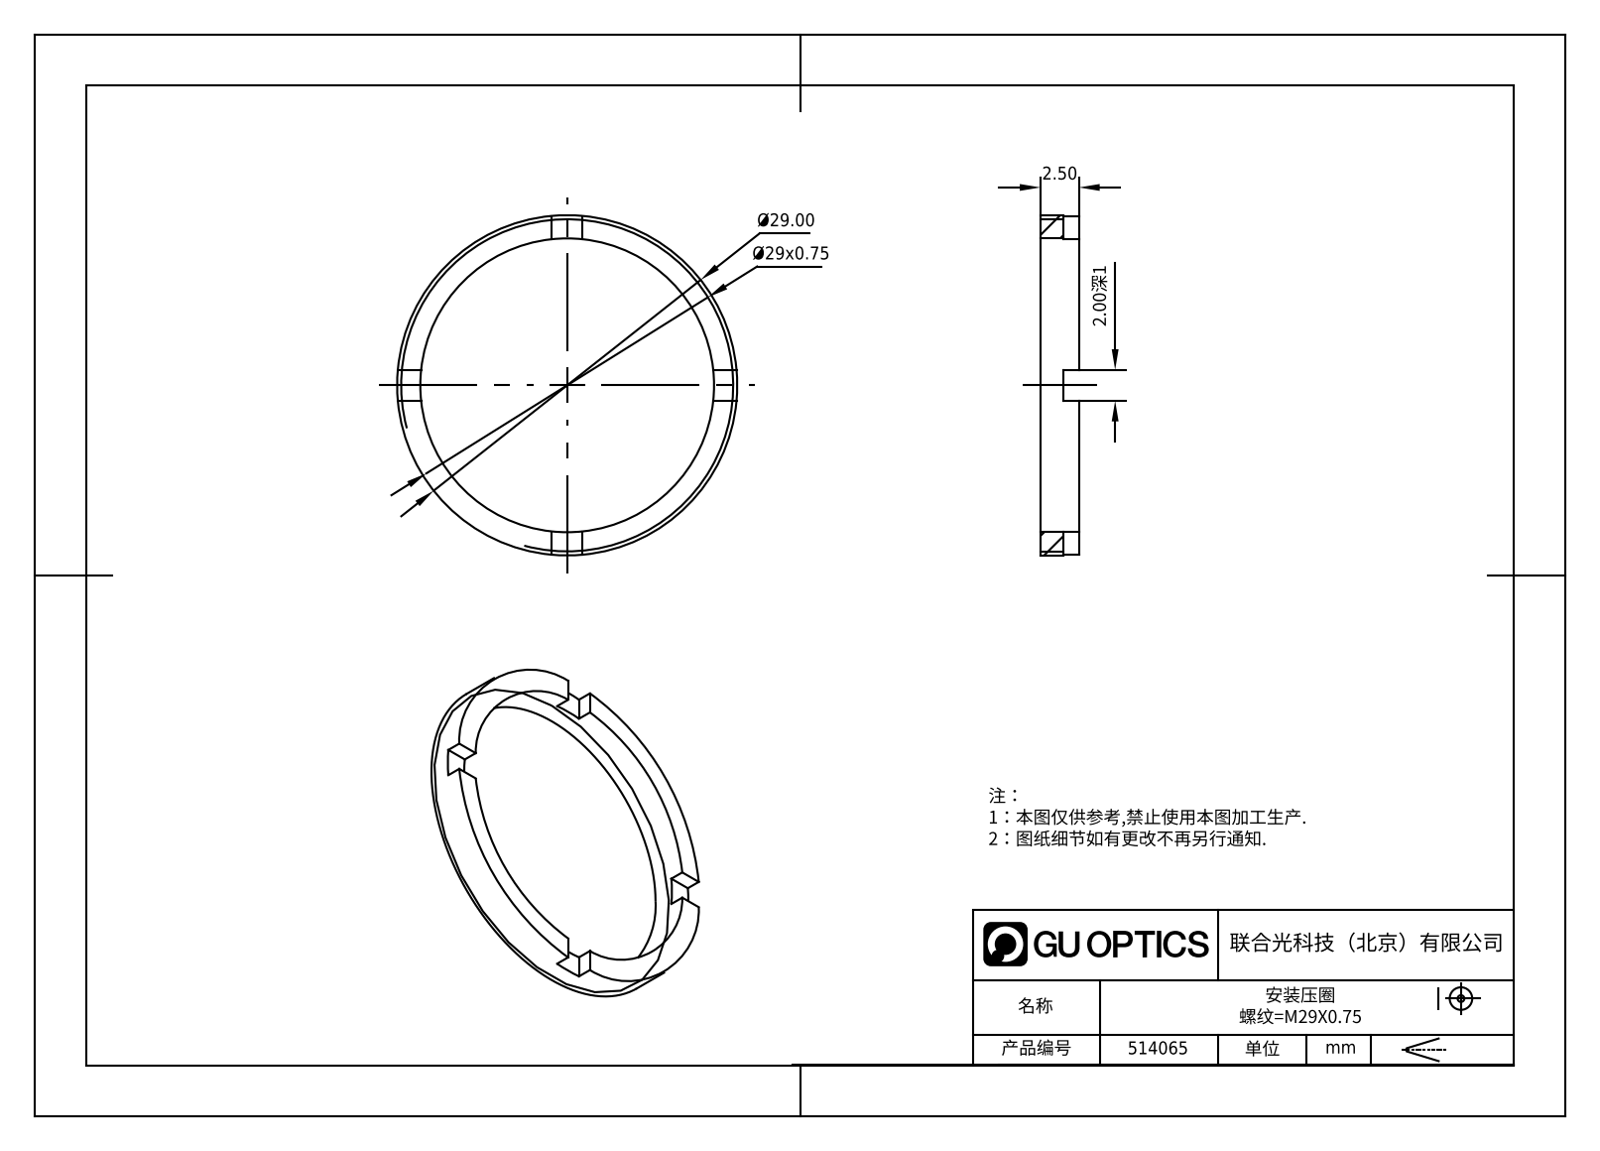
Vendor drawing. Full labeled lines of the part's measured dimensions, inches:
Part name (STEP PRODUCT): 514065
STEP written by: SolidWorks 2020 (CONFIG_CONTROL_DESIGN)
Units: inches
Bodies: 1 solid, 21 faces (17 planar, 4 cylindrical, 0 other)
Overall size (bounding box): 1.142 × 1.142 × 0.098
Volume: 0.019 in³ · Surface area: 1.06 in²
Round holes (diameter × count): ⌀1.024 ×1
Round bosses / shafts (diameter × count): ⌀1.142 ×1
Main face-to-face distances: 0.098, 0.059, 0.039, 0.079
